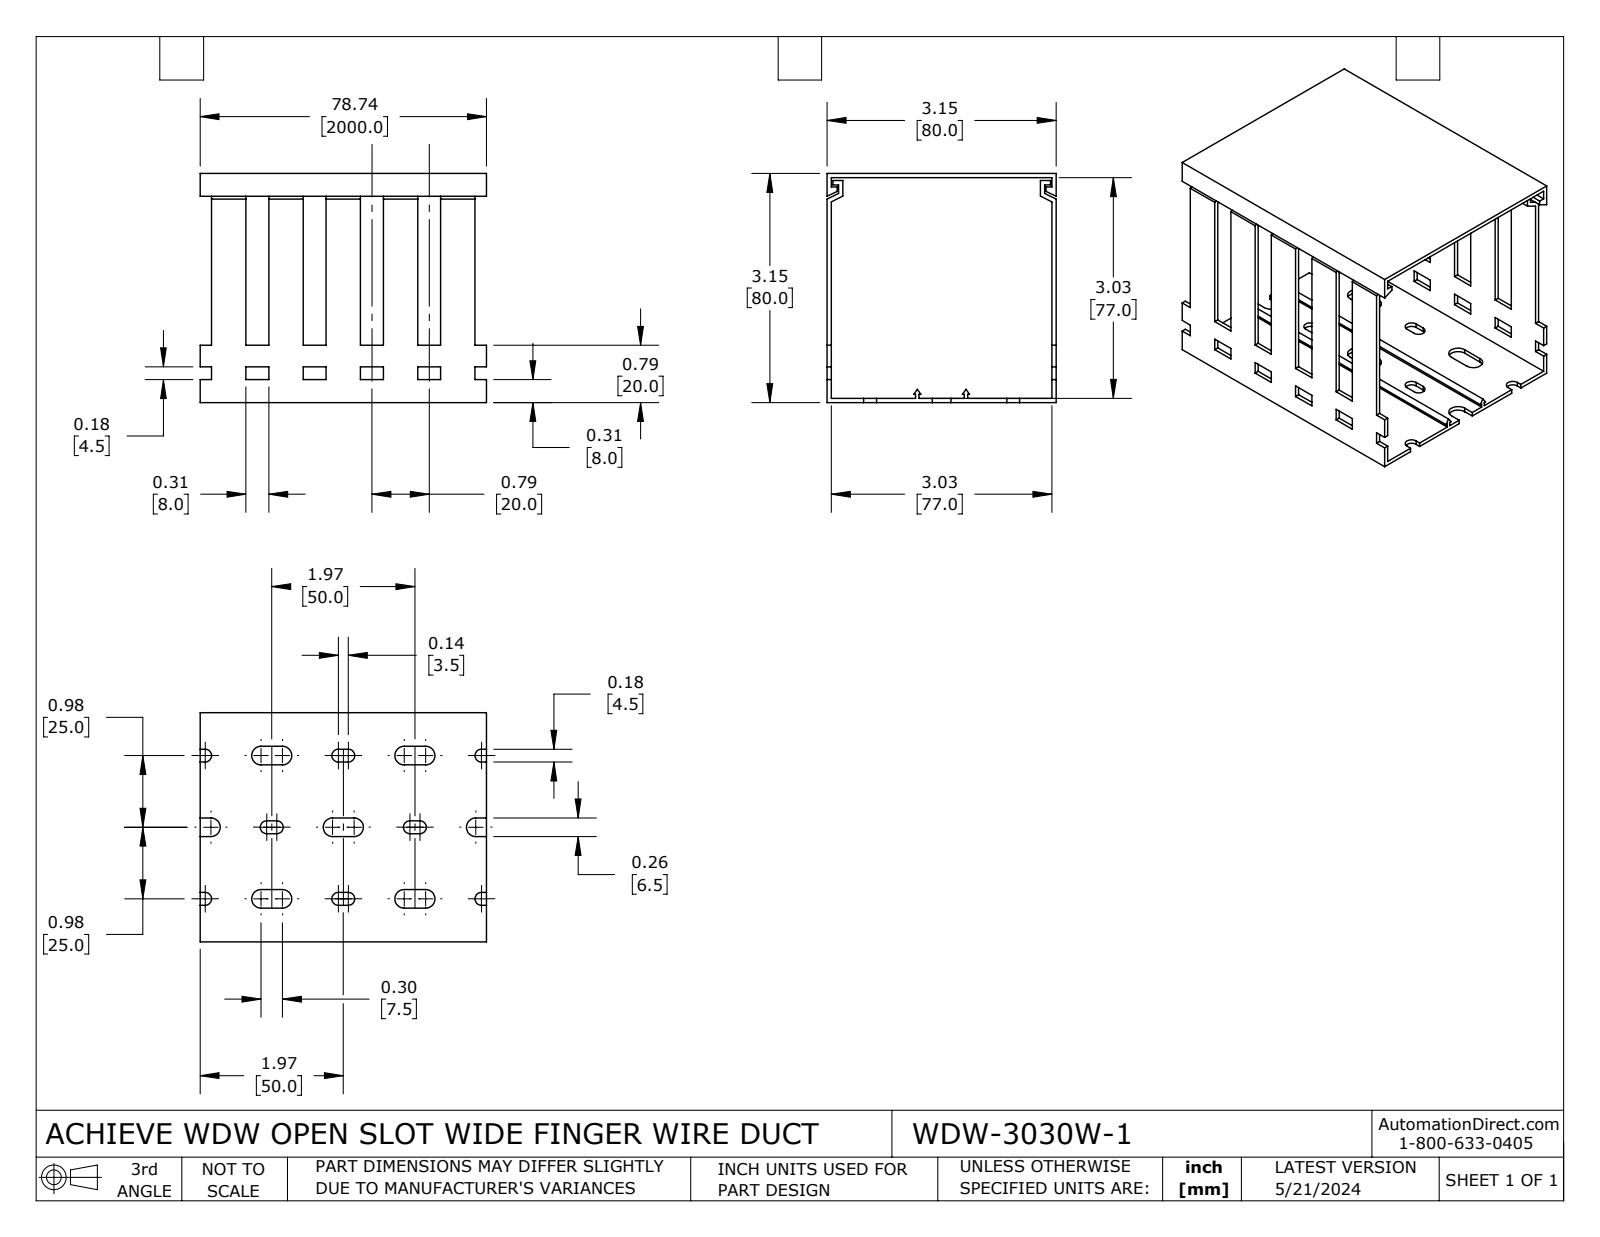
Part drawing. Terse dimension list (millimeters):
name: WDW-3030W-1
written by: SolidWorks 2023 (CONFIG_CONTROL_DESIGN)
unit: mm
bodies: 2 solids, 258 faces (222 planar, 36 cylindrical, 0 other)
size: 100 × 80 × 80
volume: 42 551 mm³; area: 60 682 mm²
rounds: 12× R2.25, 12× R3.25
face distances: 1.5, 78.5, 80, 77, 20, 4, 76, 74.5, 40, 12
